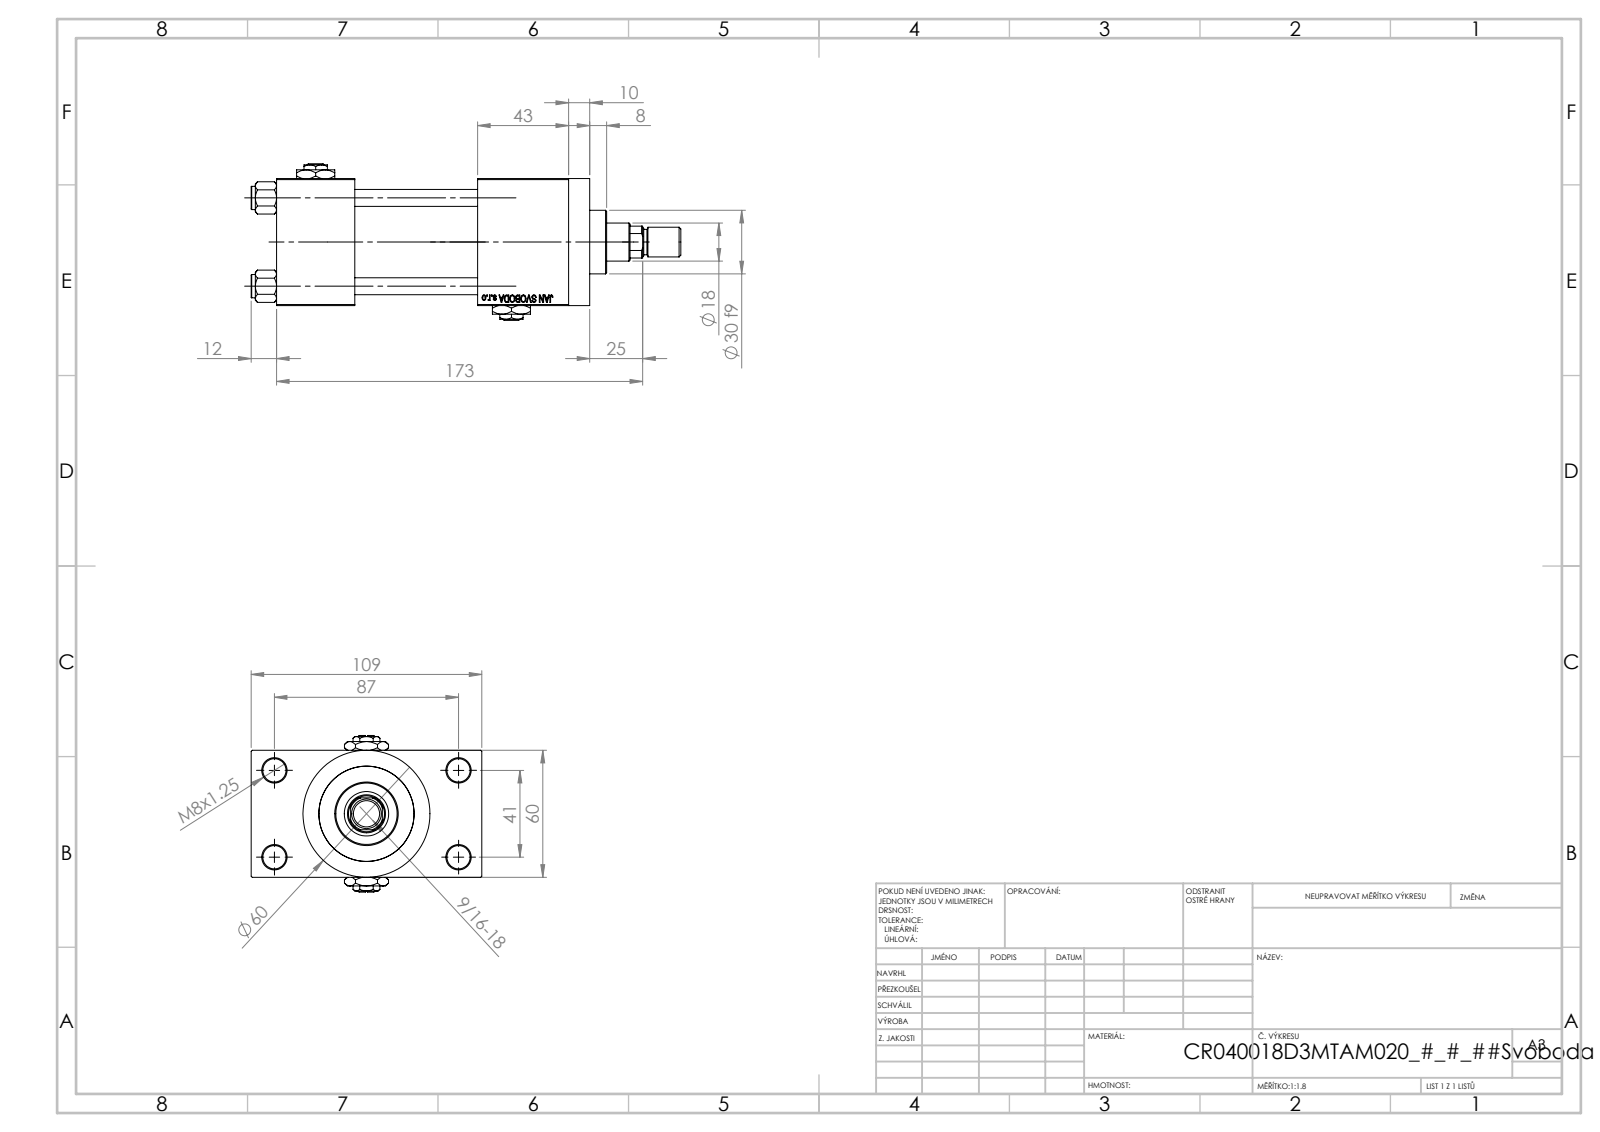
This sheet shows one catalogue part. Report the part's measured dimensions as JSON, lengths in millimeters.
{"part_name": "Zatka_pro_OIL_PORT; V215CR_VCP_D; V215CR_D_TYCINKA; V215CR_D_Body (+3 more)", "step_written_by": "SolidWorks 2019 (CONFIG_CONTROL_DESIGN)", "units": "millimeters", "bodies": {"solids": 14, "faces": 1203, "planar": 546, "cylindrical": 93, "other": 564}, "overall_size": [203, 109, 74], "volume_mm3": 523326, "surface_area_mm2": 124204, "round_holes": [[8, 4], [11, 4], [7, 2], [16.66, 2], [24, 2], [8.5, 1], [18, 1], [21, 1], [31, 1], [40, 1], [45, 1]], "round_bosses_or_shafts": [[11, 4], [60, 1], [46, 1], [30, 1], [14, 1], [12, 1]], "partial_cylinders_radius": [[8.5, 1]], "face_to_face_distances": [60, 24.5, 84.5, 58, 37, 95, 43, 138, 101, 109], "hole_center_spacings": [22.65, 29.49, 41.7, 47.15, 48.09, 64.35, 76.49, 41]}
